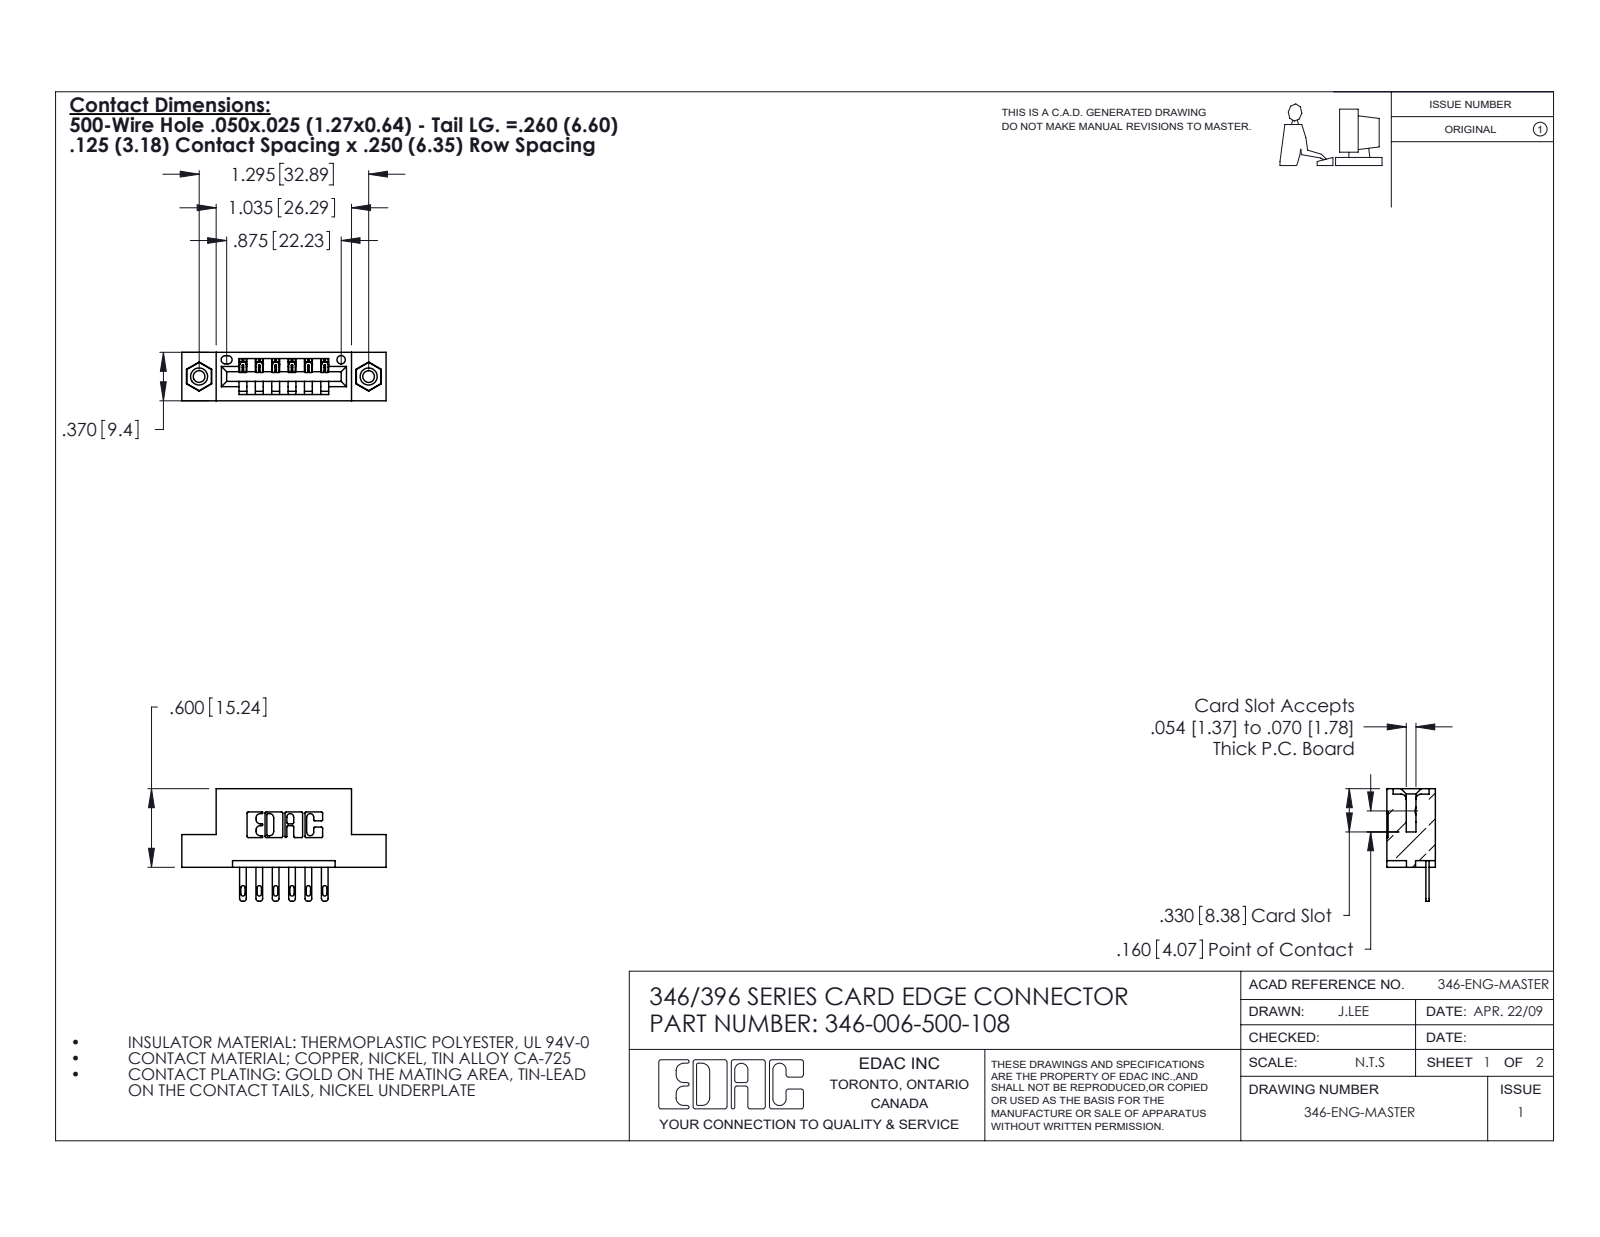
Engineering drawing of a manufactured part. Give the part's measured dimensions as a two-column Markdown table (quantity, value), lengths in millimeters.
| quantity | value |
| --- | --- |
| part name | 345-250-001_345-250-003-102; 346 Part_Flush Mounting Lugs - 0.156 Dia-TI; 346-006-500-108; 345-292-001_345-293-100 |
| STEP written by | SolidWorks 2020 (CONFIG_CONTROL_DESIGN) |
| units | millimeters |
| bodies | 9 solids, 506 faces (312 planar, 178 cylindrical, 16 other) |
| overall size | 39.6 × 21.8 × 9.4 |
| volume | 3 540 mm³ |
| surface area | 4 074 mm² |
| round holes (diameter × count) | 2.3 × 2, 3.2 × 2, 4 × 2, 1.6 × 1 |
| round bosses / shafts (diameter × count) | 3.9 × 2 |
| partial cylindrical surfaces (radius × count) | 0.3 × 22, 0.2 × 12, 0.4 × 12, 0.5 × 12, 0.2 × 6, 0.8 × 6, 0.7 × 3, 0.8 × 2 |
| main face-to-face distances | 6.4, 9.4, 1.2, 8.2, 1.8, 7.6, 0.6, 3.8, 5.6, 2.5 |
| hole center spacings | 6.2, 27.7, 32.9 |
